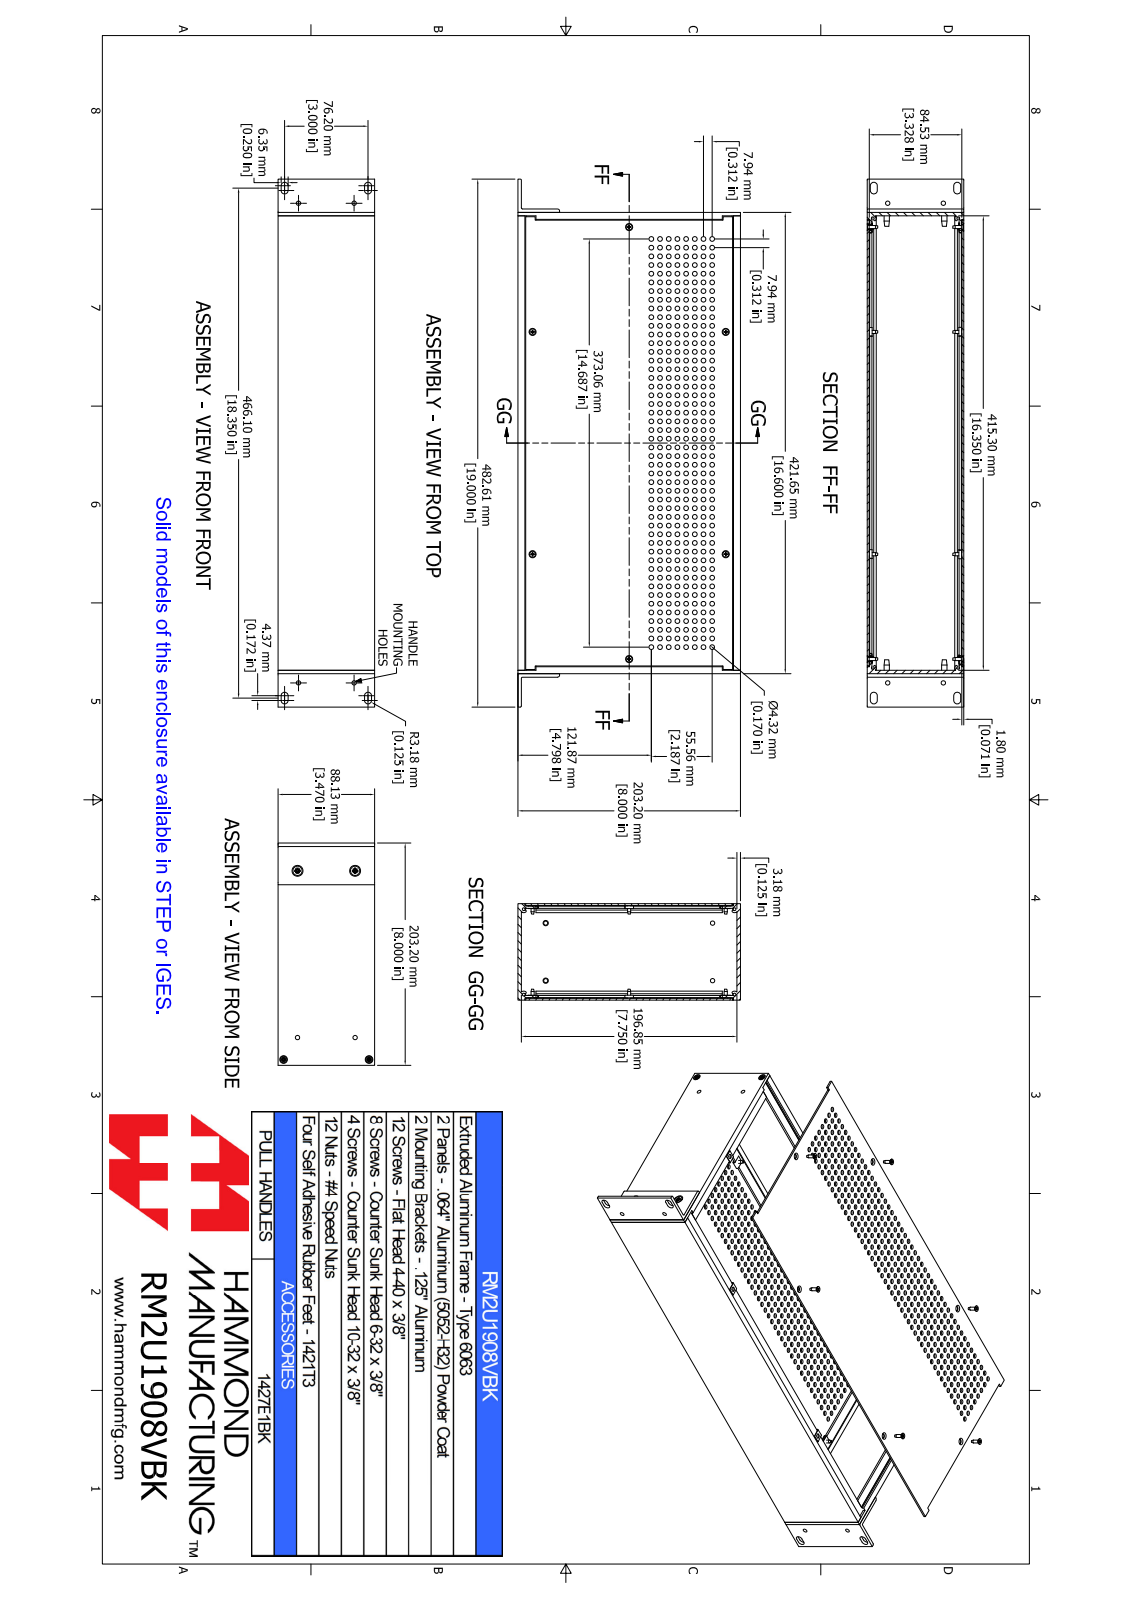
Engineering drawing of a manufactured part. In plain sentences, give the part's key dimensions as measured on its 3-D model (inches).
The part is named "RM2U1908VBK". Its 3-D file was written by "SolidWorks 2021 (AUTOMOTIVE_DESIGN)". It is 44 solids with 1950 faces: 564 planar, 954 cylindrical and 432 other. Overall it measures 19 by 8 by 3.47 inches. Its volume is 45.38 cubic inches and its surface area 1 008 square inches. Round holes: 384 of diameter 0.17, 6 of diameter 0.098, 6 of diameter 0.157, 6 of diameter 0.169, 4 of diameter 0.138, 4 of diameter 0.156, 4 of diameter 0.157, 2 of diameter 0.197. Round bosses or shafts: 6 of diameter 0.214, 6 of diameter 0.112, 4 of diameter 0.238, 4 of diameter 0.138, 2 of diameter 0.333, 2 of diameter 0.19. Partial cylindrical surfaces (rounded edges, fillets, slot ends): 18 of radius 0.039, 16 of radius 0.125, 12 of radius 0.049, 8 of radius 0.05, 6 of radius 0.037, 4 of radius 0.038, 2 of radius 0.079. The main face-to-face distances are 0.071, 3.399, 3.47, 3.328, 0.125, 0.125, 8, 7.875, 7.75, 7.875. The hole center spacings are 0.699, 0.313, 0.625, 0.988, 1.289, 0.312, 0.442, 0.698.
